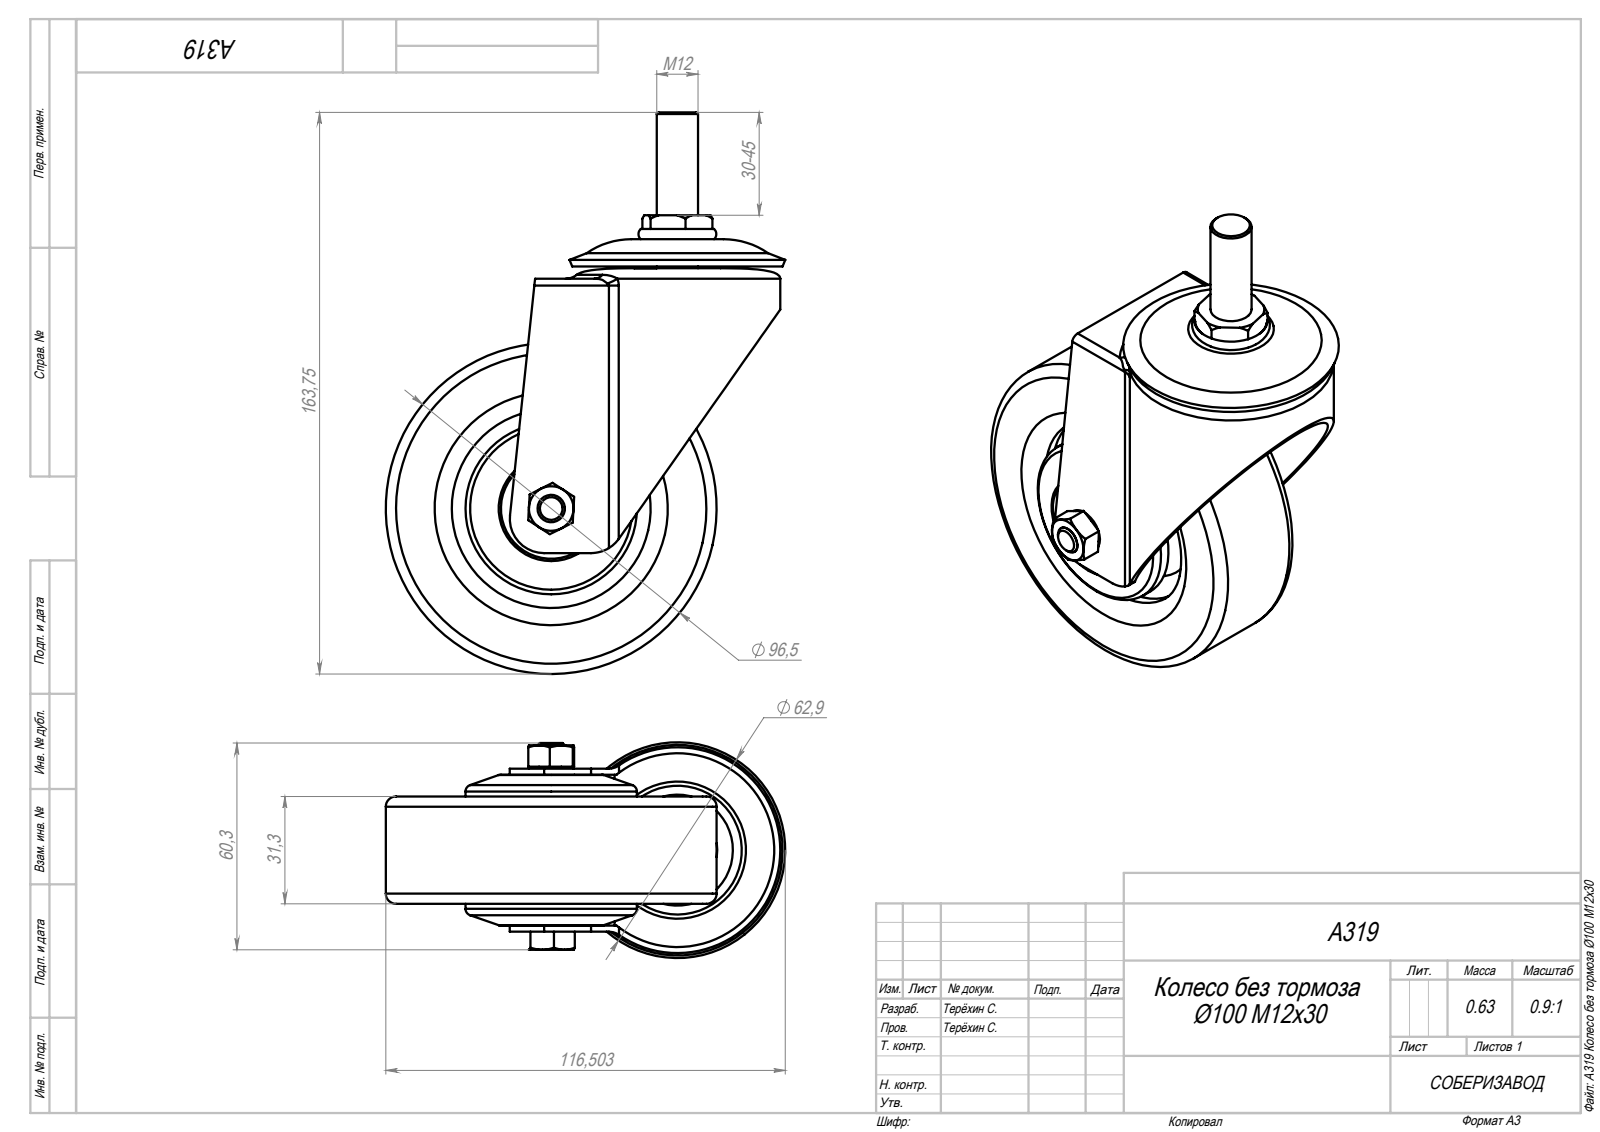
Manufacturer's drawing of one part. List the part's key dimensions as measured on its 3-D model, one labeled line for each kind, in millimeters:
Part name (STEP PRODUCT): Болт_00; hex nut style 1 gradeab_din_Hexagon Nut ISO 4032 - M8 - W - N; A319 Колесо без тормоза O100 М12х30; Крышка_00 (+5 more)
STEP written by: SolidWorks 2018 (AUTOMOTIVE_DESIGN)
Units: millimetres
Bodies: 9 solids, 246 faces (84 planar, 59 cylindrical, 103 other)
Overall size (bounding box): 163.75 × 116.5 × 62.9
Volume: 213 587 mm³ · Surface area: 79 197 mm²
Round holes (diameter × count): ⌀6.8 ×1, ⌀8 ×1, ⌀12 ×1, ⌀46 ×1, ⌀58 ×1
Round bosses / shafts (diameter × count): ⌀96.5 ×1, ⌀50 ×1, ⌀16 ×1, ⌀13 ×1
Partial cylindrical surfaces — rounded edges, fillets, slot ends (radius × count): R2 ×4, R5 ×2, R10 ×2, R28.25 ×1, R30 ×1
Main face-to-face distances: 6.35, 37.65, 1.75, 8.1, 39.4, 45.75, 13, 26.4, 21.1, 19.35
